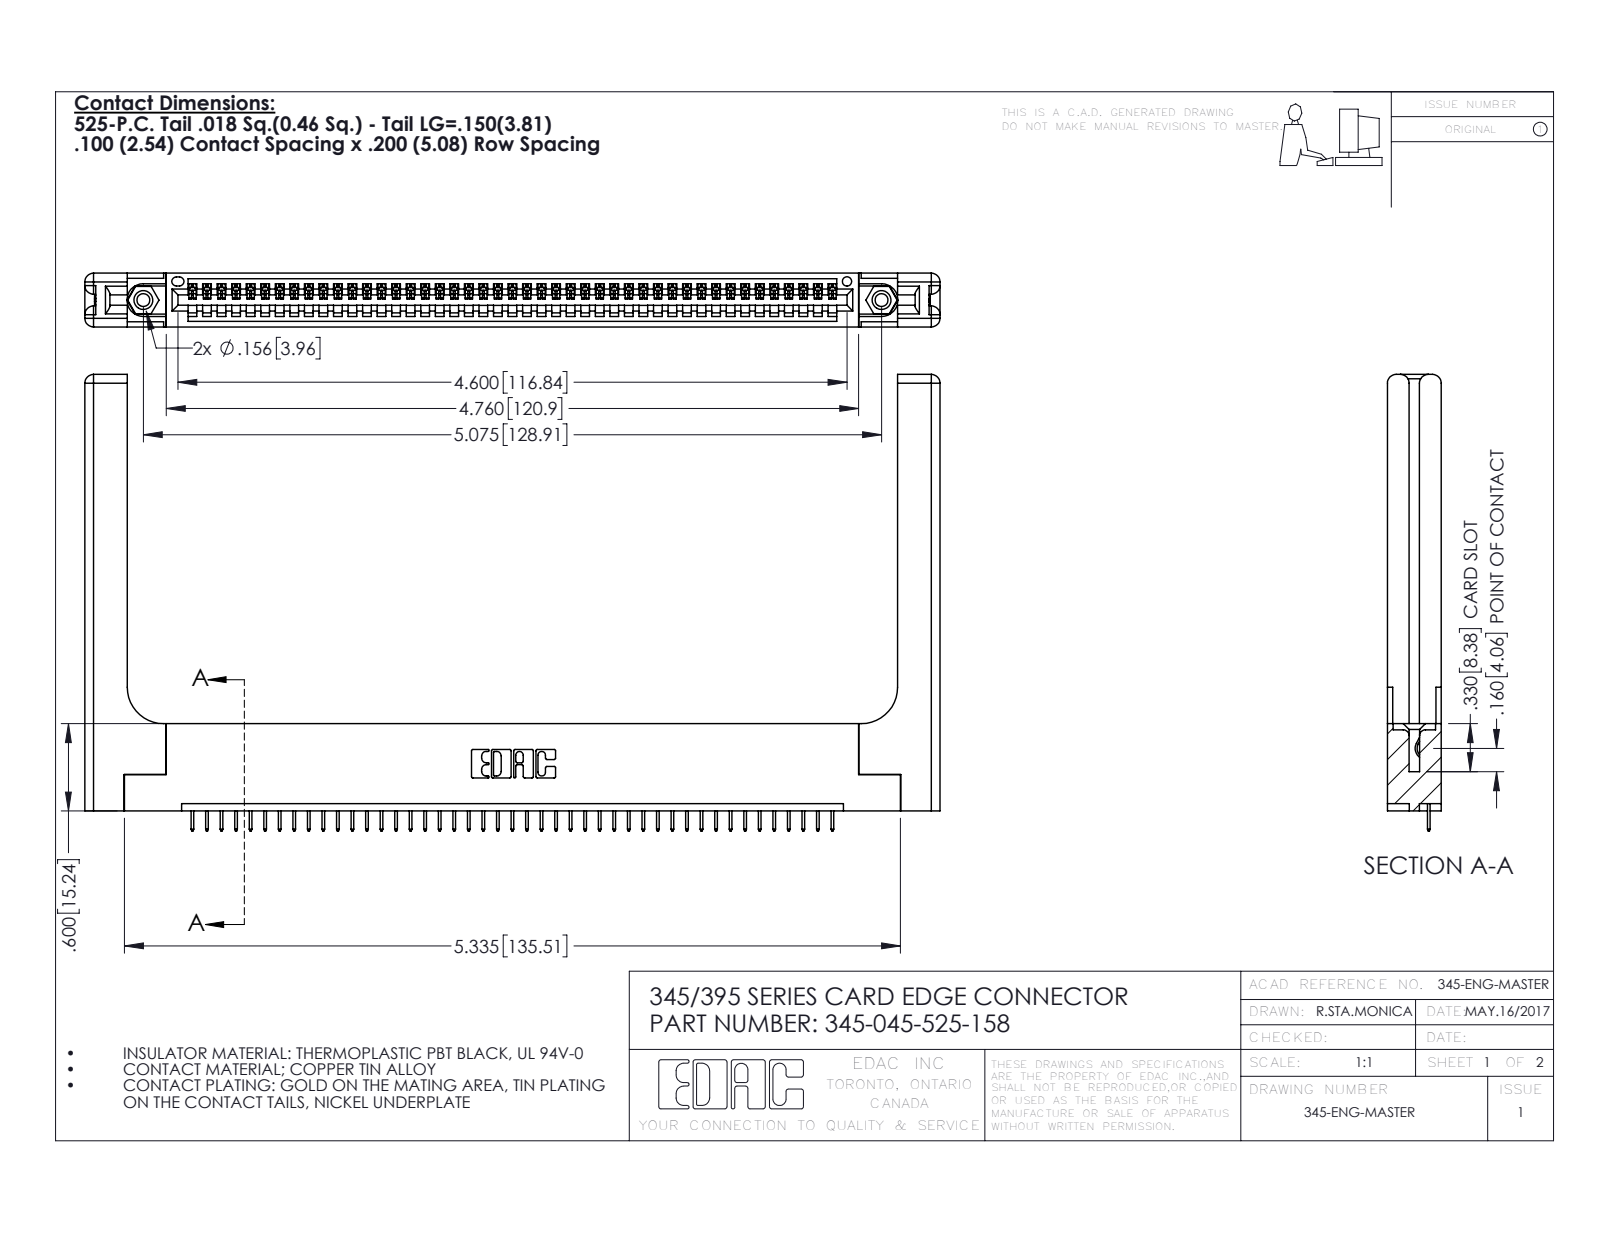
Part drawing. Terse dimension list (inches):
name: 345 Part_Flush Mounting Lugs - 0.156 Dia-TH; 345-292-001_345-293-125; 345-250-001_345-250-001-102; 345-220-058_345-220-058 (+1 more)
written by: SolidWorks 2020 (CONFIG_CONTROL_DESIGN)
unit: in
bodies: 50 solids, 3172 faces (2298 planar, 814 cylindrical, 60 other)
size: 5.879 × 3.137 × 0.37
volume: 1.375 in³; area: 36.22 in²
holes: 2× ⌀0.089, 2× ⌀0.125, 2× ⌀0.156, 1× ⌀0.064
bosses: 2× ⌀0.155
rounds: 90× R0.006, 22× R0.01, 16× R0.06, 6× R0.007, 6× R0.031, 3× R0.026, 2× R0.03, 2× R0.031
face distances: 0.37, 0.072, 0.298, 0.2, 0.098, 0.272, 0.025, 0.148, 0.15, 0.225
hole spacings: 0.27, 4.839, 5.075
